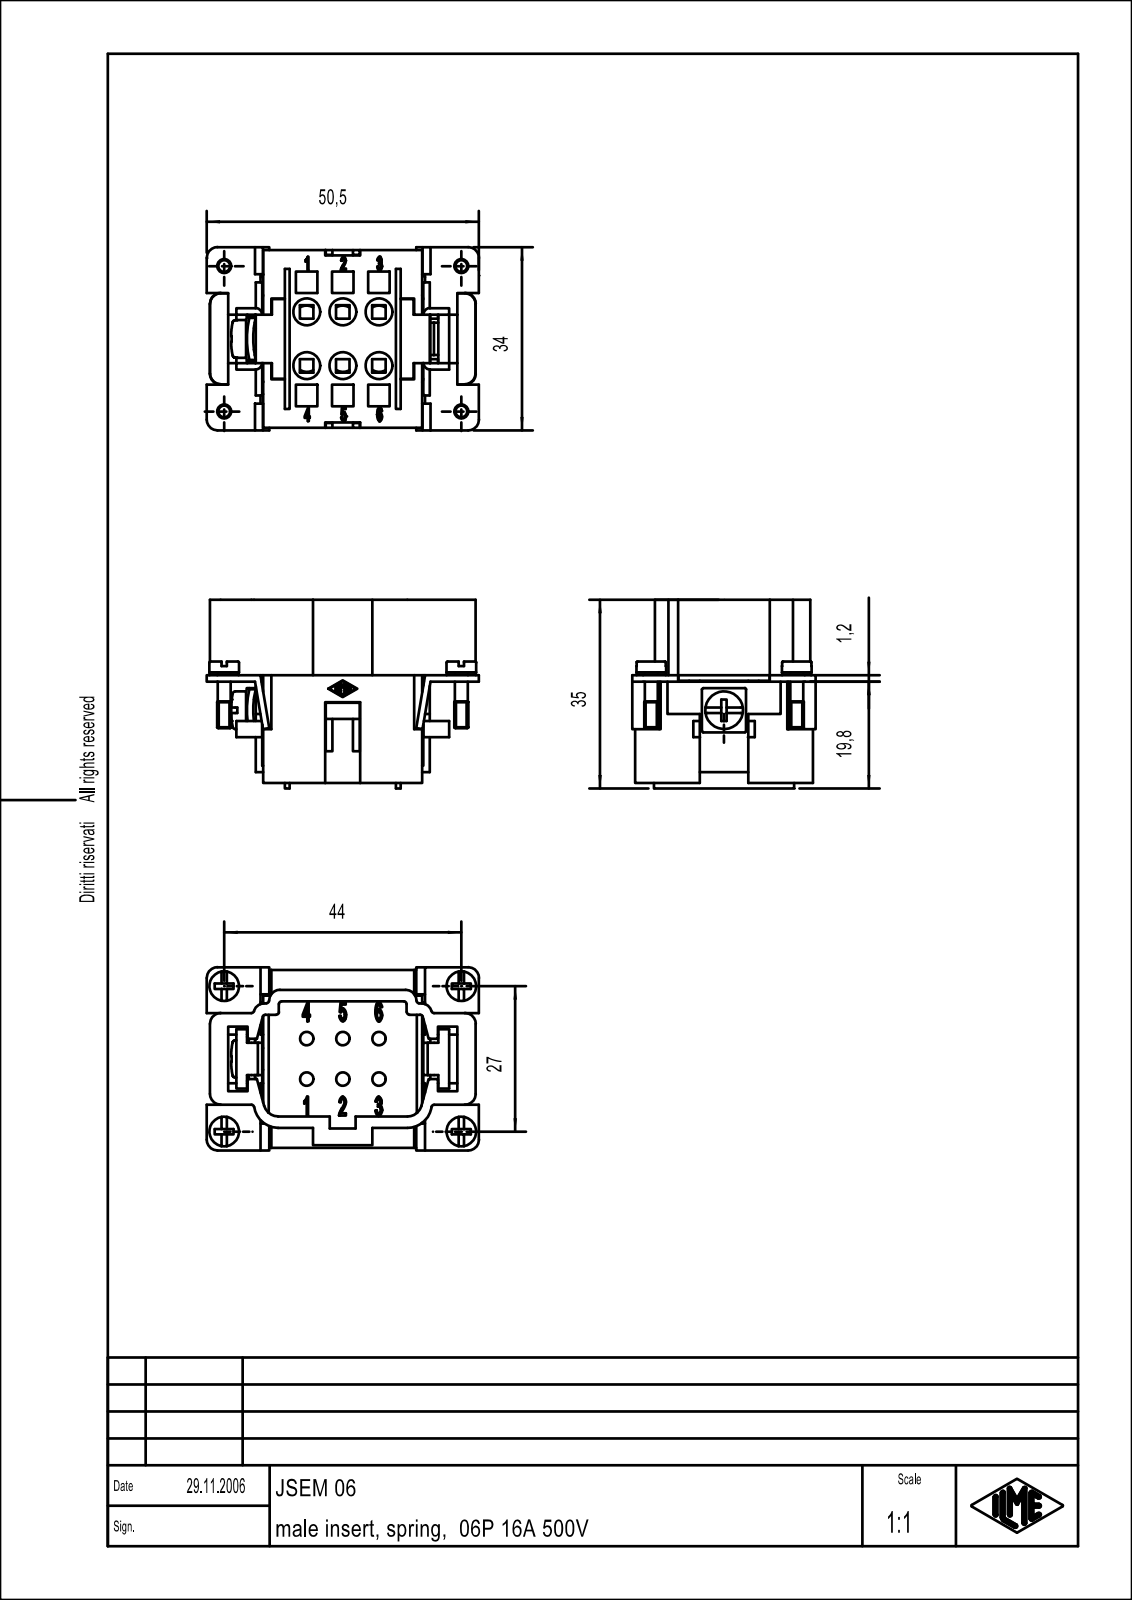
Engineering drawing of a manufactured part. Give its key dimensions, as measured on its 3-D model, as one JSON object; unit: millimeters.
{"part_name": "CSEM_Kontakteins\\S\\dtze_mit_K\\S\\dfigzugfederanschluss; JSEM_06.stp", "step_written_by": "Creo Elements/Direct Modeling 18.0B 02-Dec-2011 (C) Parametric Technology GmbH (AUTOMOTIVE_DESIGN)", "units": "millimeters", "bodies": {"solids": 1, "faces": 845, "planar": 553, "cylindrical": 144, "other": 148}, "overall_size": [50.5, 35, 34], "volume_mm3": 25190, "surface_area_mm2": 15458, "round_holes": [[5, 6], [3.24, 1]], "round_bosses_or_shafts": [[2.5, 6], [5.5, 4], [5.4, 4], [2.6, 4], [2.4, 4], [7, 1], [4, 1]], "partial_cylinders_radius": [[2, 16], [0.1, 14], [0.5, 12], [2.4, 6], [1.25, 4], [0.2, 2], [1.2, 2], [1.36, 2]], "face_to_face_distances": [1.2, 8, 4, 20, 25, 2.2, 1.5, 5.8, 27.2, 18.8], "hole_center_spacings": [6.7, 12.04, 10, 13.4, 16.72]}
